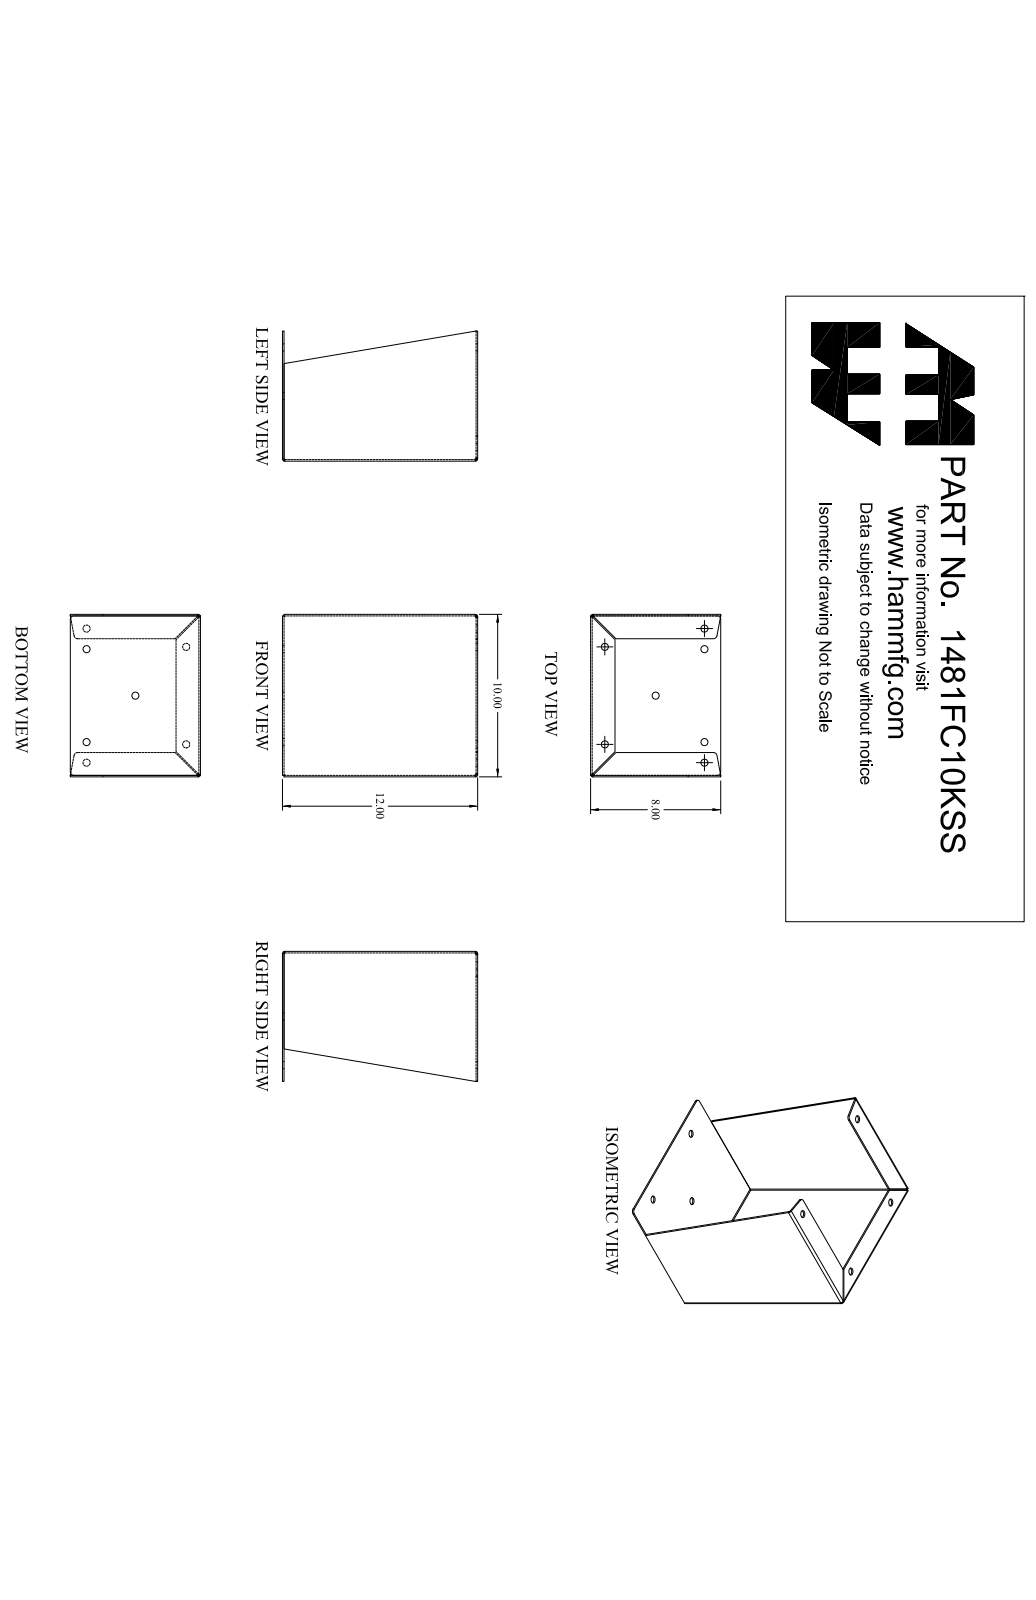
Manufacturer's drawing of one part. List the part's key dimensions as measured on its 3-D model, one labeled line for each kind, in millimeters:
Part name (STEP PRODUCT): 1481FC10KSS_Default
STEP written by: SolidWorks 2019 (CONFIG_CONTROL_DESIGN)
Units: millimetres
Bodies: 1 solid, 78 faces (42 planar, 30 cylindrical, 6 other)
Overall size (bounding box): 304.8 × 254 × 203.2
Volume: 607 100 mm³ · Surface area: 509 500 mm²
Round holes (diameter × count): ⌀11.1 ×7
Partial cylindrical surfaces — rounded edges, fillets, slot ends (radius × count): R1.2 ×6, R3.6 ×6, R5.6 ×4
Main face-to-face distances: 2.4, 251.6, 249.2, 254, 2.4, 300, 302.4, 302.4, 304.8, 35.7
Hole centre spacings: 32.2, 105.3, 110, 129.6, 155.6, 158.2, 177.4, 215.3
